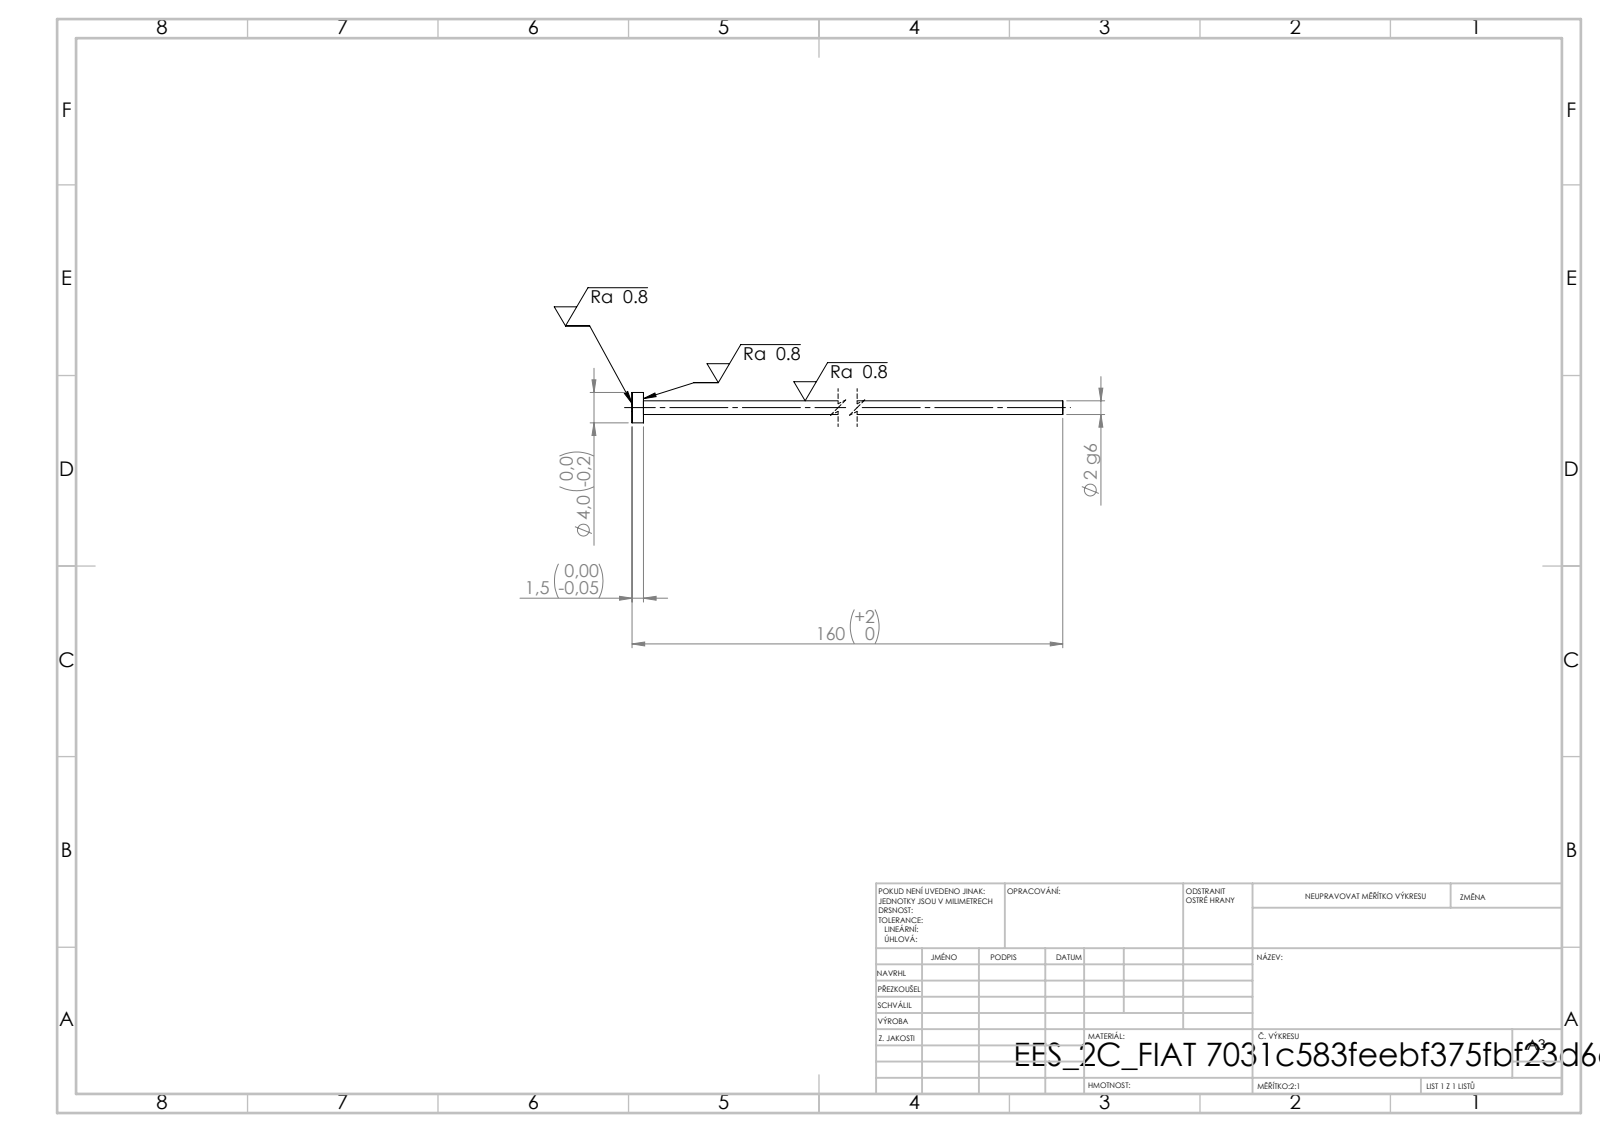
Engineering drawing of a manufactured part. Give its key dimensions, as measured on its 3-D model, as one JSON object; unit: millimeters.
{"step_written_by": "SolidWorks 2019 (CONFIG_CONTROL_DESIGN)", "units": "millimeters", "bodies": {"solids": 1, "faces": 7, "planar": 3, "cylindrical": 4, "other": 0}, "overall_size": [160, 4, 4], "volume_mm3": 422, "surface_area_mm2": 940, "round_bosses_or_shafts": [[4, 1], [1.8, 1]], "face_to_face_distances": [1.5, 160, 158.5]}
